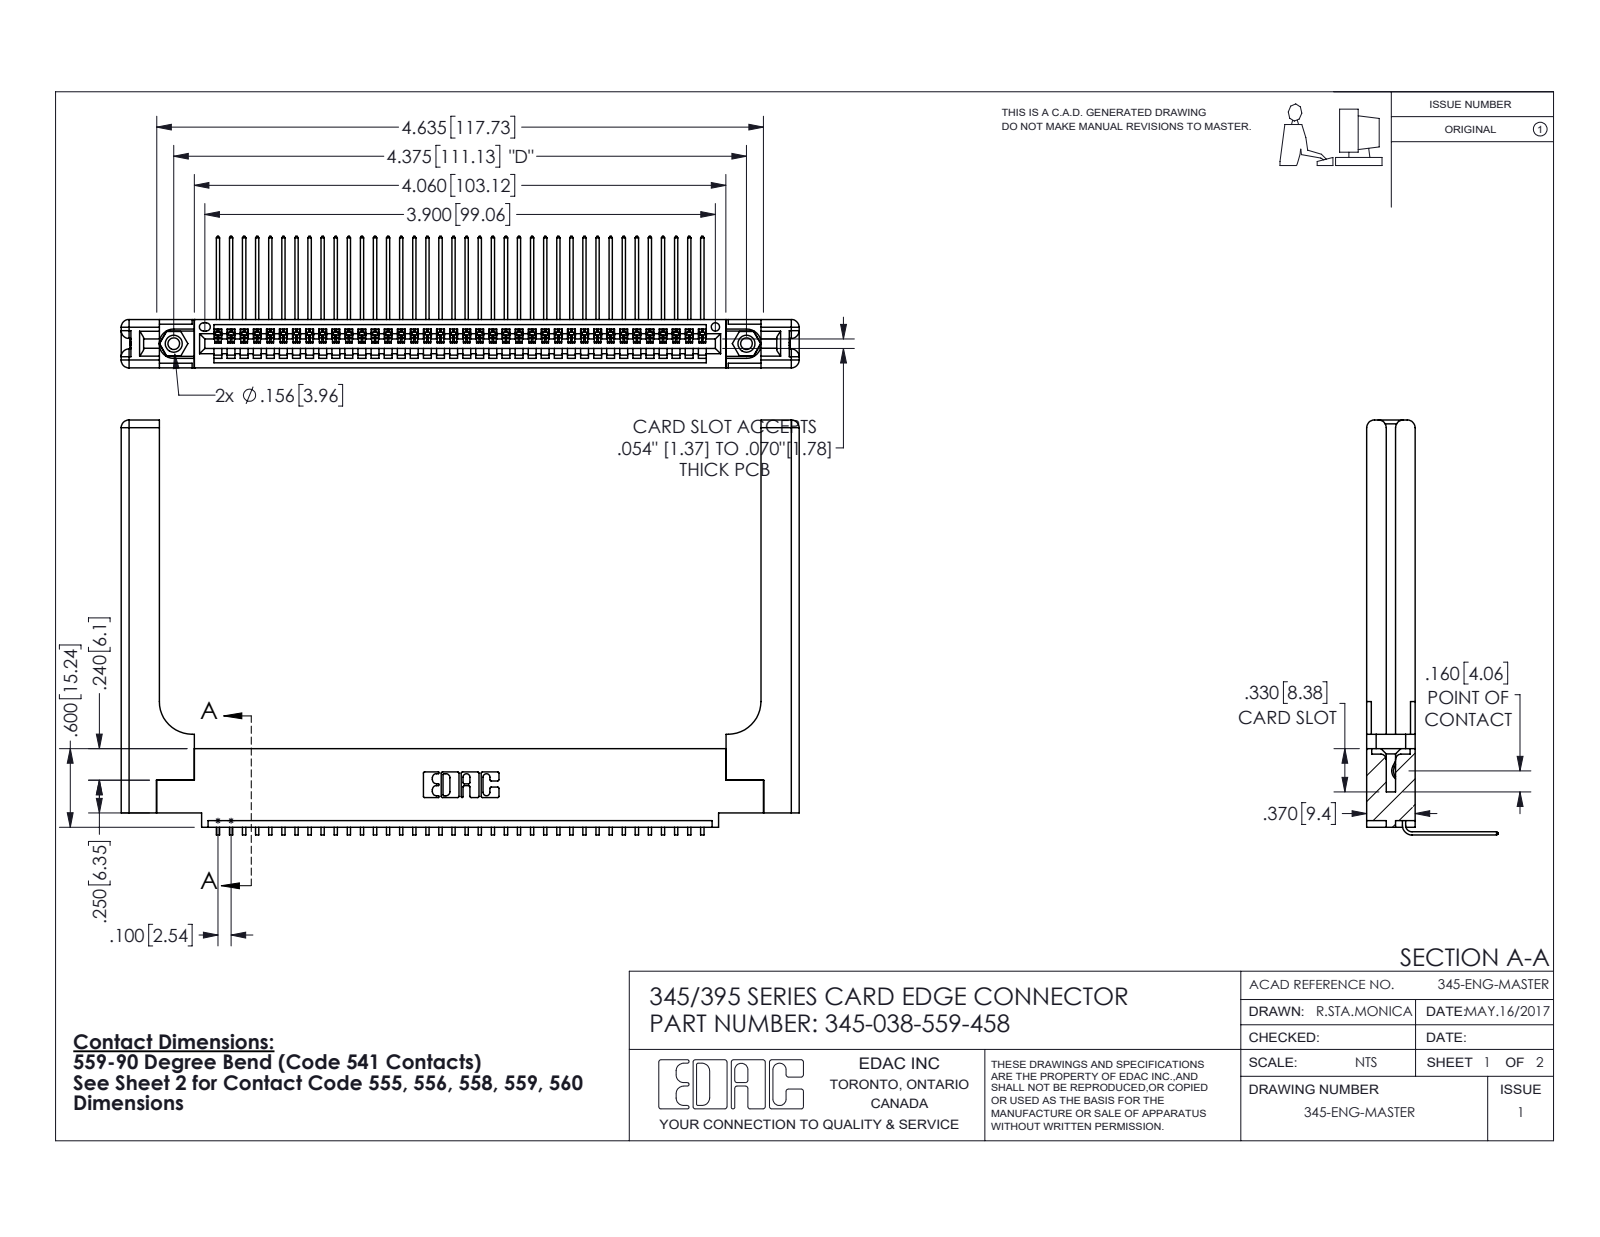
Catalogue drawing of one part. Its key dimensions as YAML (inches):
part_name: "345-220-058_345-220-058; 345 Part_0.110 Offset - 0.156 Dia-TH; 345-292-001_558 559 Tail - 1; 345-038-559-458 (+1 more)"
step_written_by: "SolidWorks 2016 (CONFIG_CONTROL_DESIGN)"
units: inches
bodies: {solids: 43, faces: 2666, planar: 1828, cylindrical: 778, other: 60}
overall_size: [5.179, 3.169, 1.005]
volume: 1.283
surface_area: 35.2
round_holes:
  - {diameter: 0.089, count: 2}
  - {diameter: 0.125, count: 2}
  - {diameter: 0.156, count: 2}
  - {diameter: 0.064, count: 1}
round_bosses_or_shafts:
  - {diameter: 0.155, count: 2}
partial_cylinders:
  - {radius: 0.006, count: 76}
  - {radius: 0.01, count: 22}
  - {radius: 0.06, count: 16}
  - {radius: 0.007, count: 6}
  - {radius: 0.031, count: 6}
  - {radius: 0.026, count: 3}
  - {radius: 0.03, count: 2}
  - {radius: 0.031, count: 2}
face_to_face_distances: [0.37, 0.072, 0.298, 0.098, 0.272, 0.025, 0.2, 0.148, 0.15, 0.225]
hole_center_spacings: [0.27, 4.139, 4.375]
